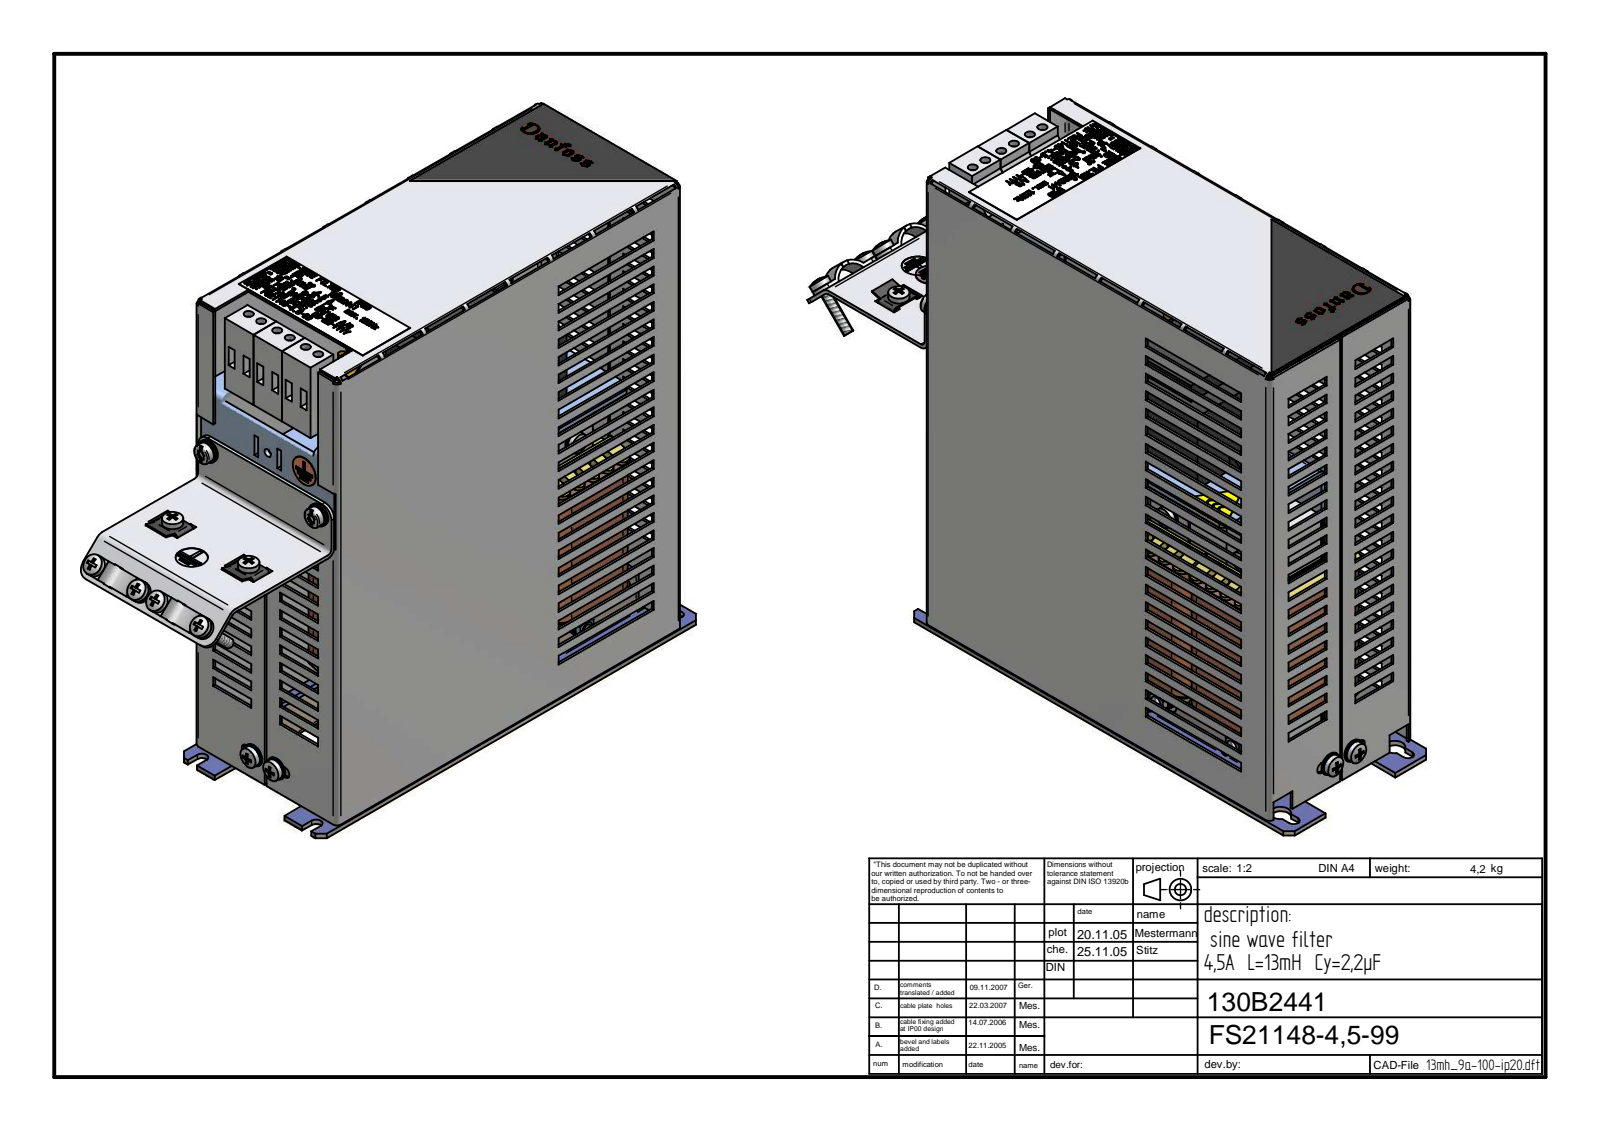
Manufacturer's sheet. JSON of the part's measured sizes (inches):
{"step_written_by": "Unknown (CONFIG_CONTROL_DESIGN)", "units": "inches", "bodies": {"solids": 190, "faces": 10173, "planar": 6412, "cylindrical": 965, "other": 2796}, "overall_size": [10.816, 9.705, 8.081], "volume_in3": 120.6, "surface_area_in2": 1953, "round_holes": [[0.13, 29], [0.177, 21], [0.169, 13], [0.016, 8], [0.128, 8], [0.15, 8], [0.315, 4], [0.108, 3], [0.157, 3], [0.161, 3], [0.197, 3], [0.012, 2]], "round_bosses_or_shafts": [[0.157, 19], [0.315, 18], [0.354, 12], [0.295, 7], [0.346, 4], [0.472, 3], [0.303, 3], [0.827, 2]], "partial_cylinders_radius": [[0.091, 40], [0.059, 35], [0.031, 26], [0.039, 26], [0.157, 24], [0.236, 21], [0.089, 20], [0.094, 20]], "face_to_face_distances": [0.039, 2.913, 0.571, 0.866, 1.476, 1.437, 0.787, 2.047, 0.906, 2.953], "hole_center_spacings": [0.906, 1.299, 1.181, 1.575, 0.394, 2.205, 2.362, 0.546]}
